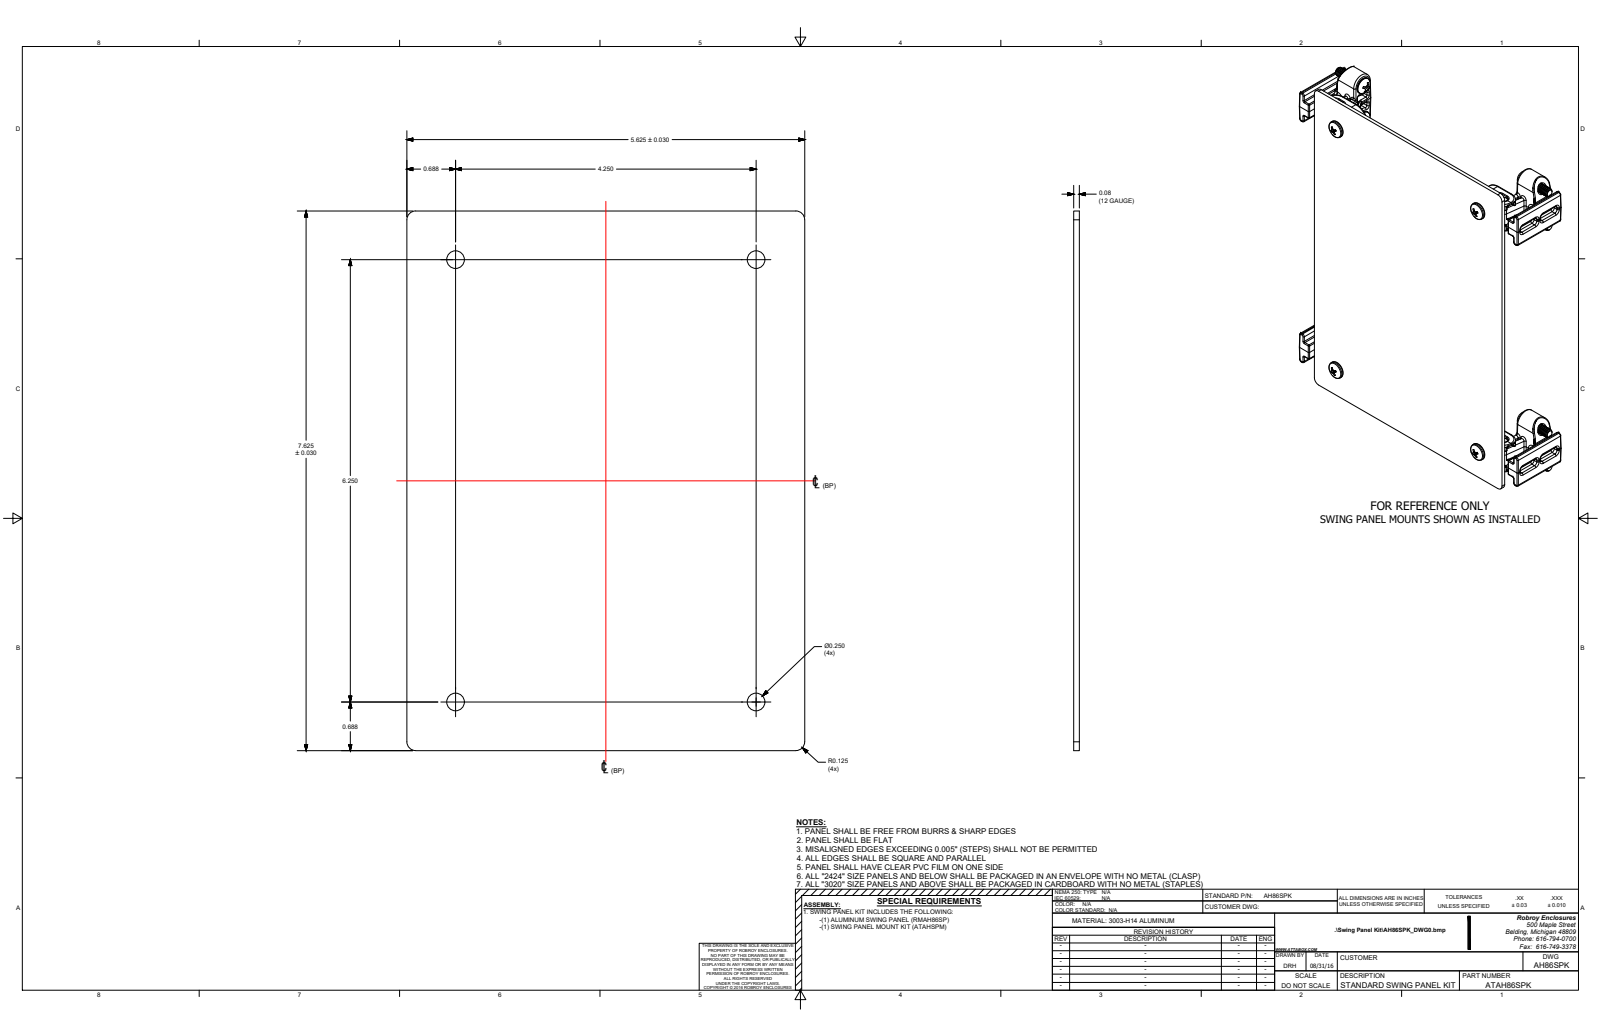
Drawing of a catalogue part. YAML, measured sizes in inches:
part_name: "AH86SPK"
step_written_by: "SolidWorks 2019 (AUTOMOTIVE_DESIGN)"
units: inches
bodies: {solids: 33, faces: 2010, planar: 518, cylindrical: 736, other: 756}
overall_size: [7.625, 6.559, 1.368]
volume: 6.502
surface_area: 145.2
round_holes:
  - {diameter: 0.156, count: 8}
  - {diameter: 0.25, count: 8}
round_bosses_or_shafts:
  - {diameter: 0.373, count: 8}
  - {diameter: 0.262, count: 8}
  - {diameter: 0.19, count: 8}
partial_cylinders:
  - {radius: 0.035, count: 248}
  - {radius: 0.02, count: 124}
  - {radius: 0.065, count: 54}
  - {radius: 0.015, count: 30}
  - {radius: 0.045, count: 16}
  - {radius: 0.05, count: 16}
  - {radius: 0.025, count: 12}
  - {radius: 0.9, count: 8}
face_to_face_distances: [0.08, 0.106, 6.25, 0.5, 0.51, 0.59, 0.72, 5.57, 5.697, 6.559]
hole_center_spacings: [6.25, 0.875, 4.25, 7.558, 5.375, 7.125]
